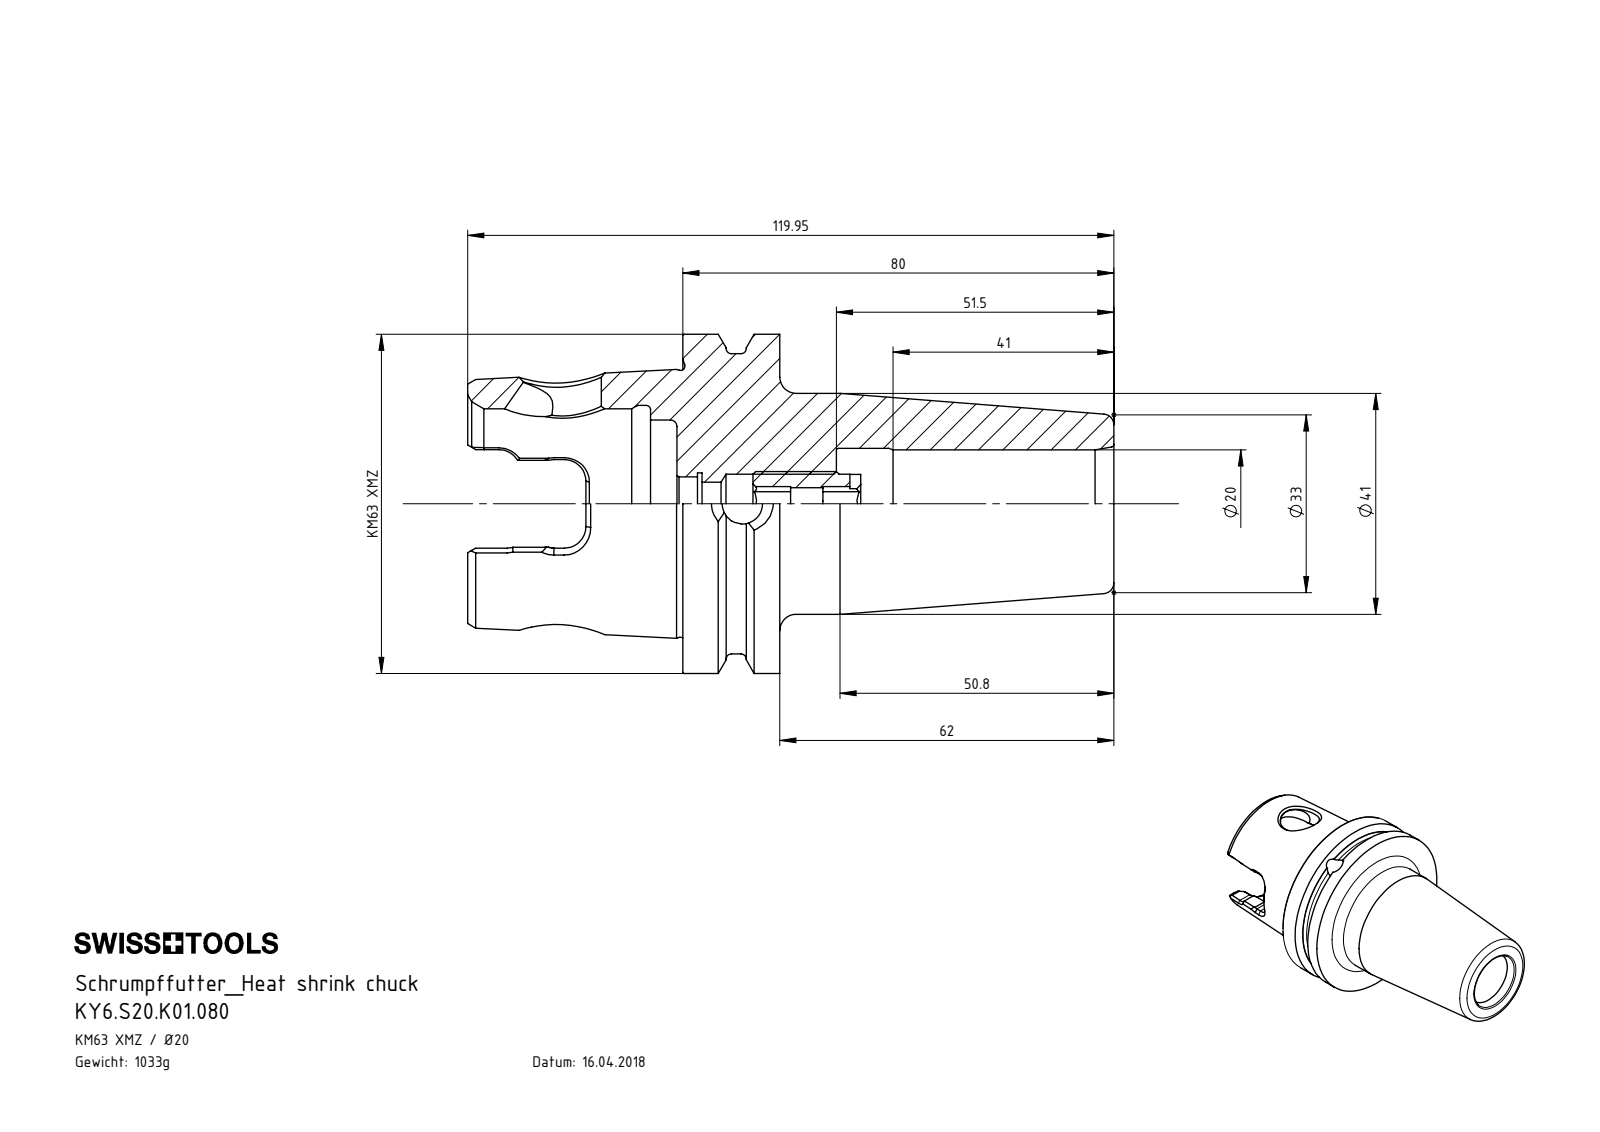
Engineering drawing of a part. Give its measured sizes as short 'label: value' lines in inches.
name: KY6-S20.K01.080_A; KY6.S20.K01.080; ERU-AN5.K01.020_A
written by: SolidWorks 2017 (CONFIG_CONTROL_DESIGN)
unit: in
bodies: 2 solids, 277 faces (79 planar, 60 cylindrical, 138 other)
size: 4.722 × 2.478 × 2.478
volume: 8.032 in³; area: 49.22 in²
holes: 2× ⌀0.294, 1× ⌀0.236, 1× ⌀0.315, 1× ⌀0.334, 1× ⌀0.394, 1× ⌀0.433, 1× ⌀0.453, 1× ⌀0.571, 1× ⌀0.787, 1× ⌀0.811, 1× ⌀1.224, 1× ⌀1.389
bosses: 1× ⌀2.478, 1× ⌀2.193, 1× ⌀1.614, 1× ⌀0.472
rounds: 6× R0.157, 2× R0.277
face distances: 0.709, 0.043, 0.752, 0.236, 3.193, 3.15, 2.441, 0.193, 0.945, 3.386
